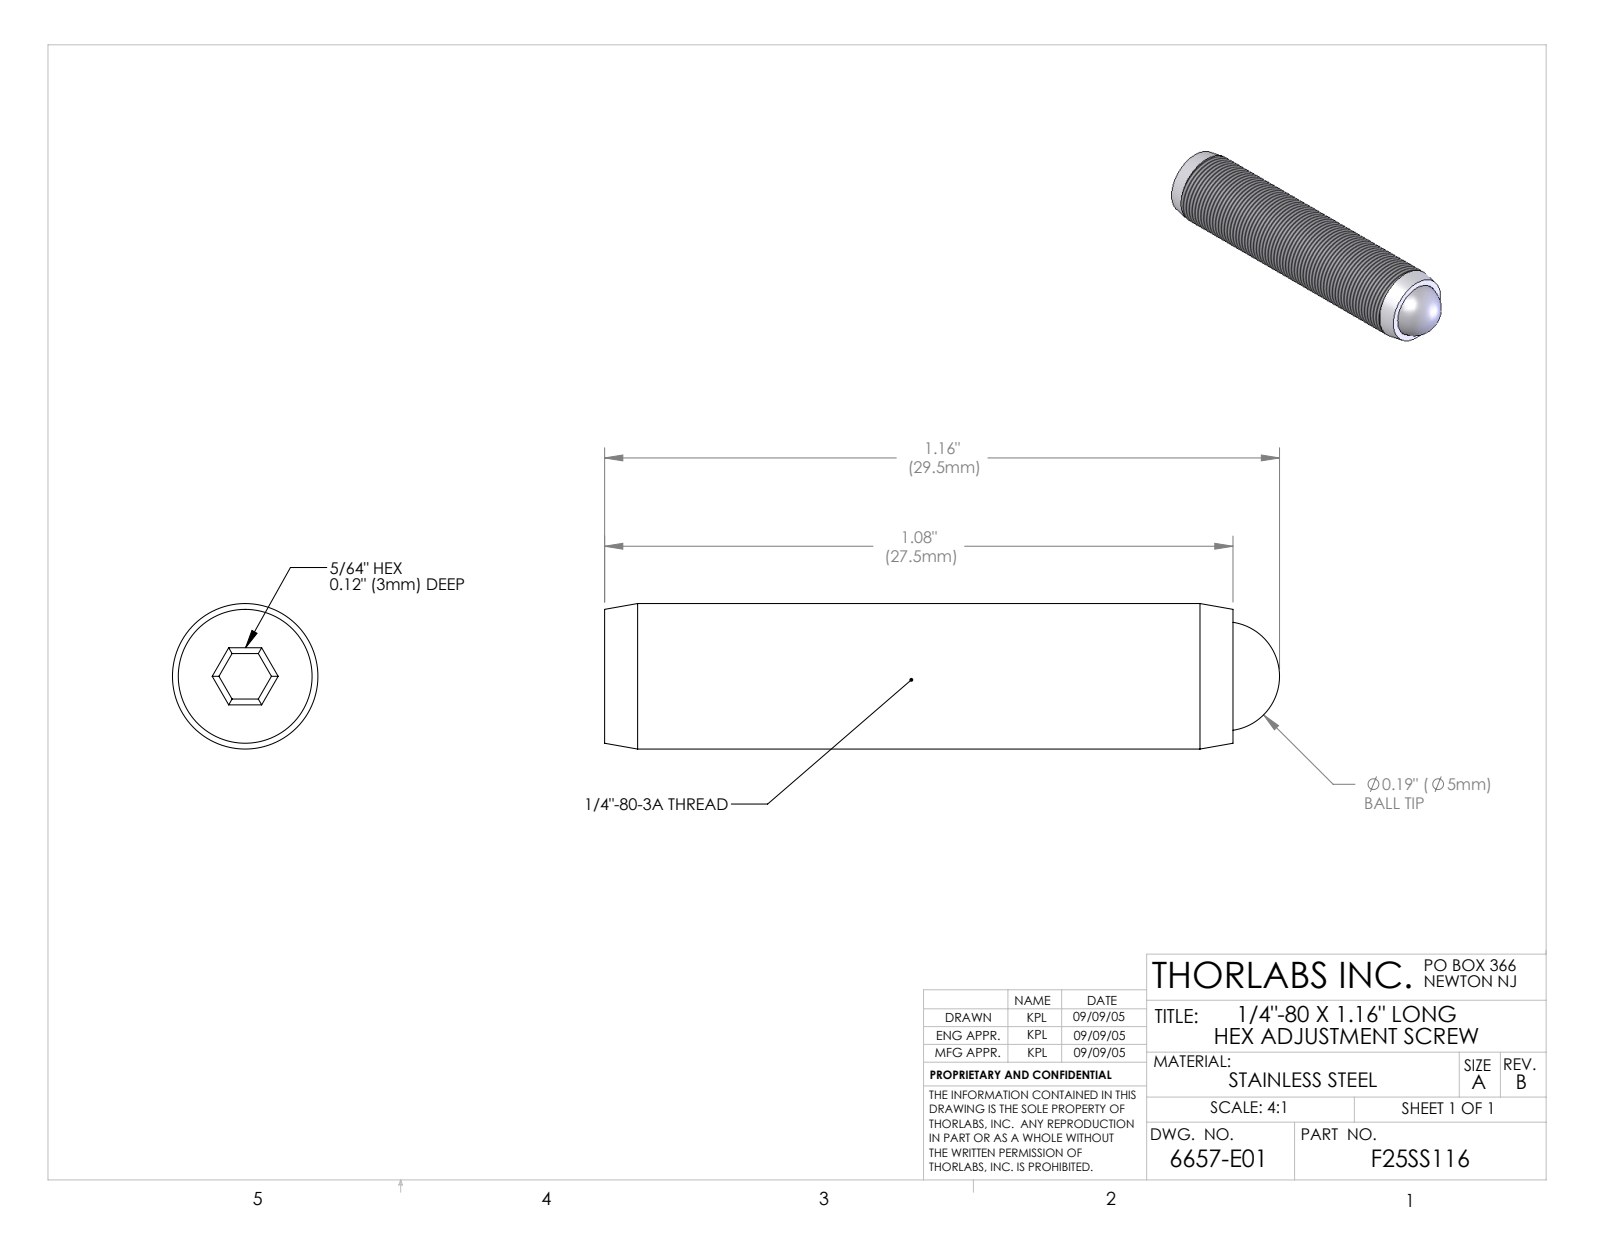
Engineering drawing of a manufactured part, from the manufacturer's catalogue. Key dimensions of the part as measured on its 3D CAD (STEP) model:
Part name (STEP PRODUCT): 6657-E0W
STEP written by: SolidWorks 2007 (AUTOMOTIVE_DESIGN)
Units: millimetres
Bodies: 2 solids, 29 faces (15 planar, 4 cylindrical, 10 other)
Overall size (bounding box): 29.46 × 6.35 × 6.35
Volume: 870 mm³ · Surface area: 718 mm²
Round holes (diameter × count): ⌀4.78 ×1
Round bosses / shafts (diameter × count): ⌀6.35 ×1
Main face-to-face distances: 27.43, 1.99, 3.04, 24.39, 1.98
